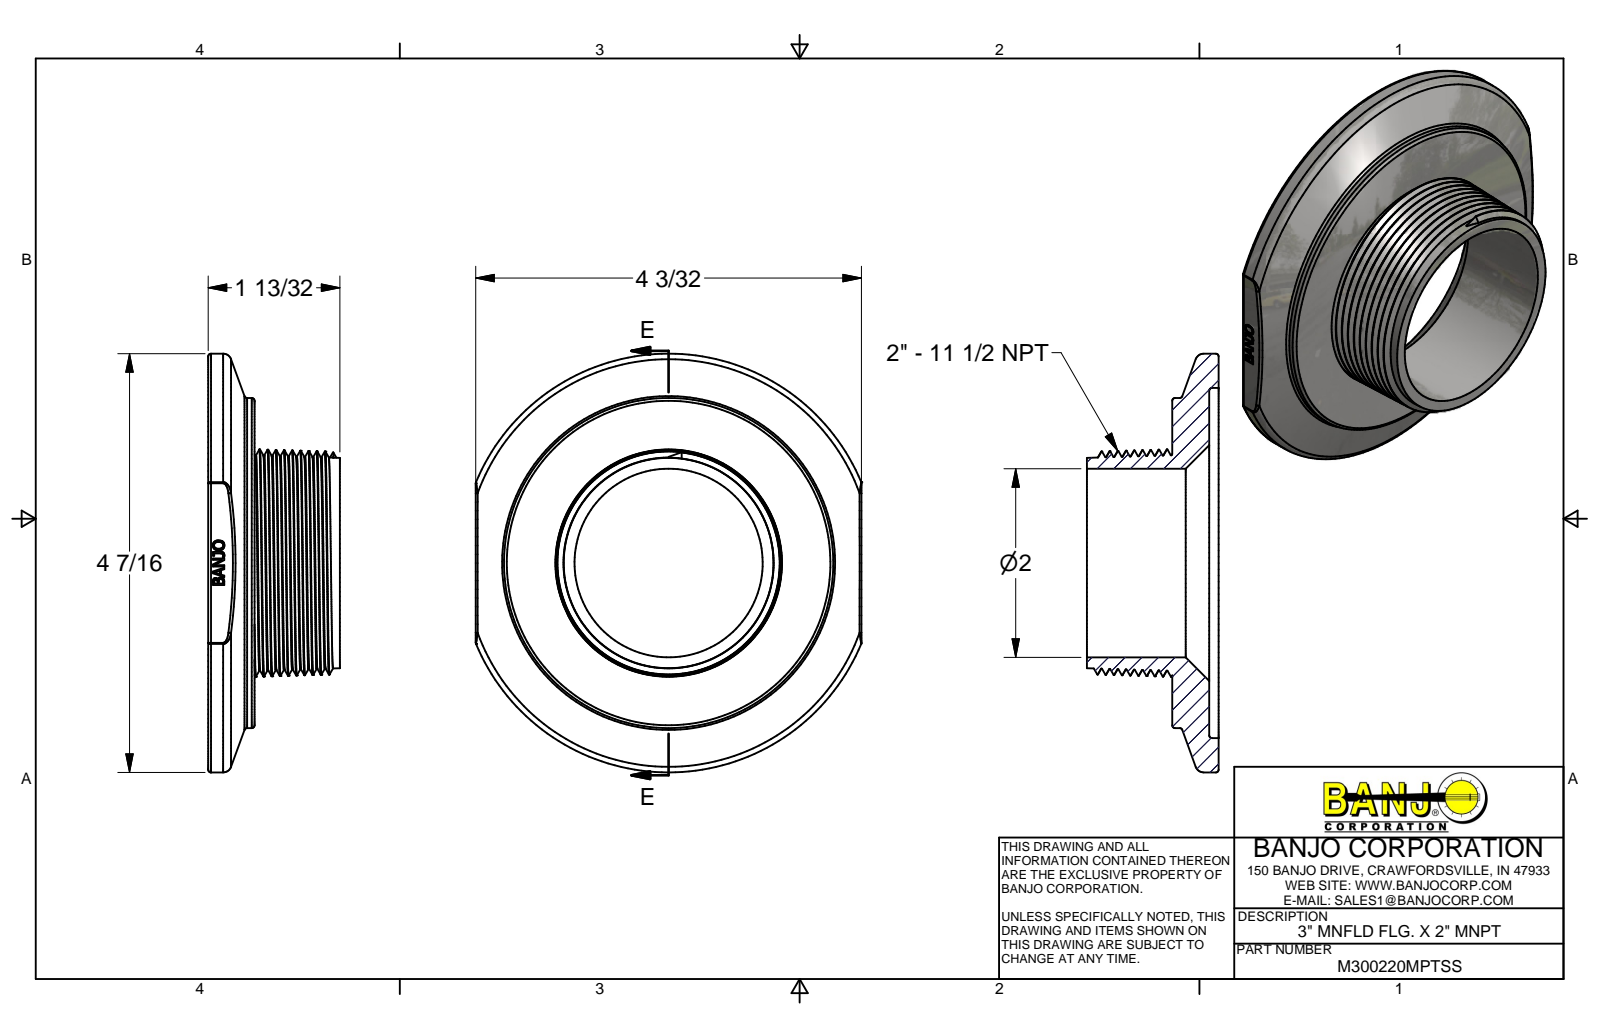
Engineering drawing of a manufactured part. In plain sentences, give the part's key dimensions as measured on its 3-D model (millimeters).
The part is named "M300220MPTSS". Its 3-D file was written by "Autodesk Inventor 2013 (AUTOMOTIVE_DESIGN)". It is 1 solid with 336 faces: 140 planar, 11 cylindrical and 185 other. Overall it measures 112.8 by 104.1 by 35.6 millimeters. Its volume is 79 590 cubic millimeters and its surface area 30 920 square millimeters. Round holes: 1 of diameter 50.8, 1 of diameter 94.3. Round bosses or shafts: 1 of diameter 88.9. Partial cylindrical surfaces (rounded edges, fillets, slot ends): 6 of radius 0.8, 1 of radius 56.4. The main face-to-face distances are 10, 12.5, 2.5, 23, 33, 35.6, 104.1, 0.8, 103.4, 102.6.
